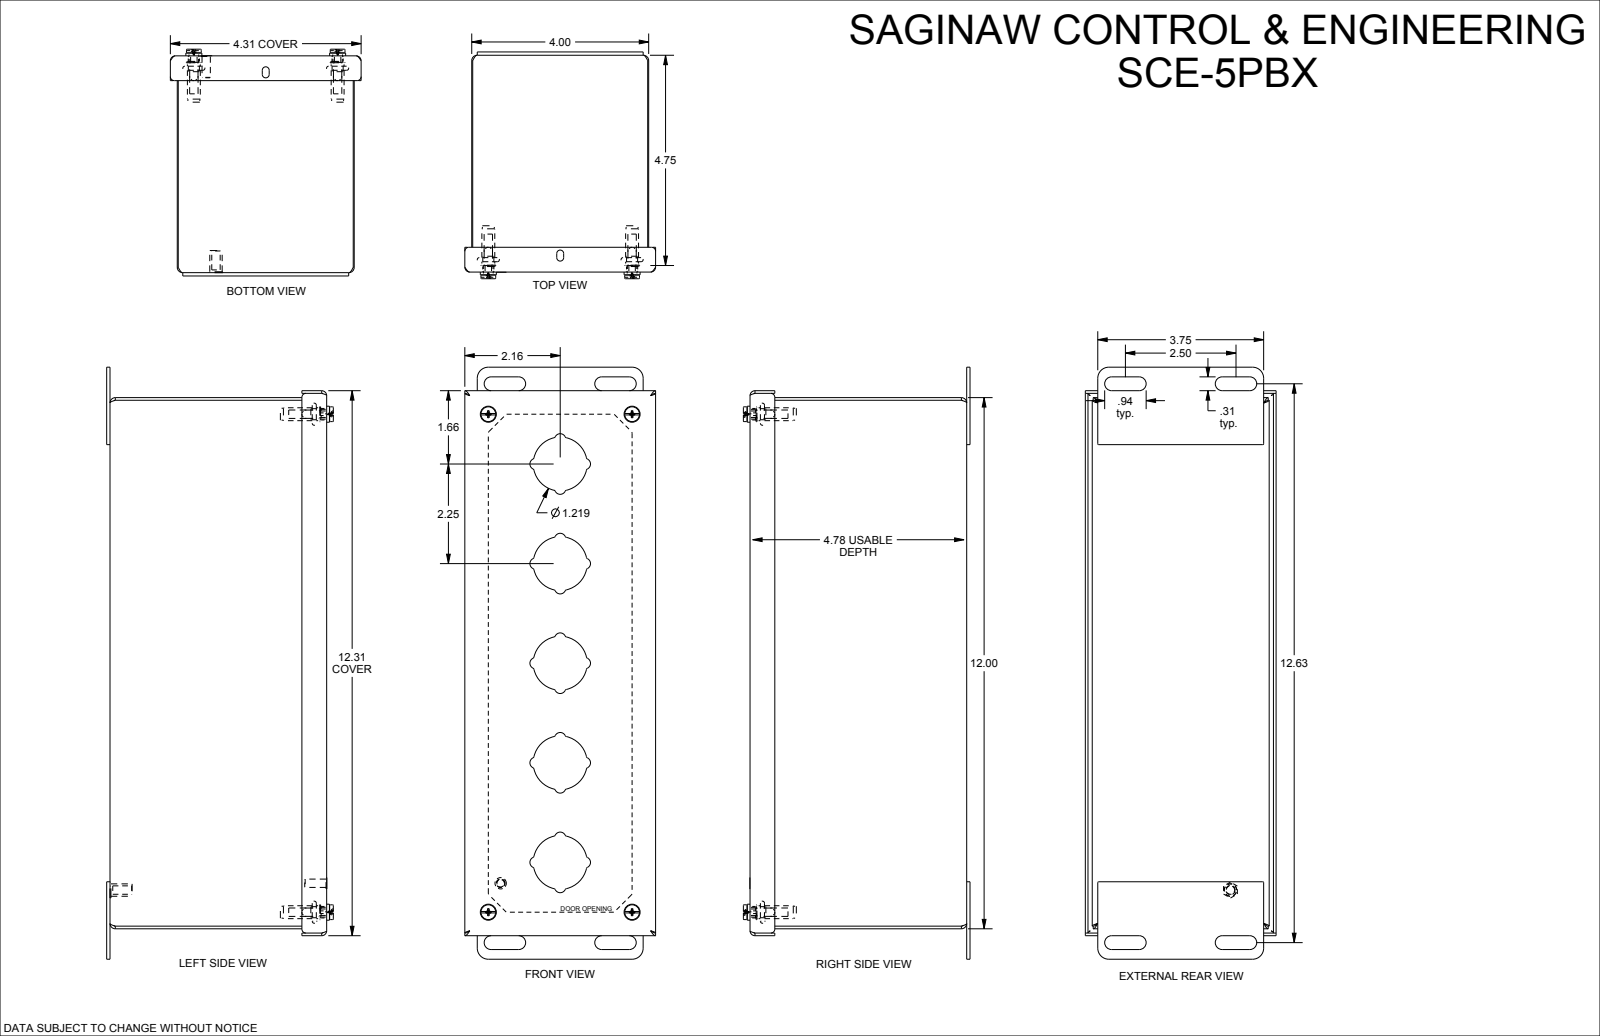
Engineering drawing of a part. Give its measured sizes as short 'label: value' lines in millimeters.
name: SCE-5PBX-RAL1018
written by: SolidWorks 2021 (AUTOMOTIVE_DESIGN)
unit: mm
bodies: 19 solids, 599 faces (209 planar, 228 cylindrical, 162 other)
size: 339.7 × 130.1 × 109.7
volume: 294 500 mm³; area: 385 900 mm²
holes: 5× ⌀4.8, 4× ⌀5.6, 4× ⌀6.4, 4× ⌀6.4, 4× ⌀8.1
bosses: 5× ⌀4.8, 4× ⌀11.1, 4× ⌀9.2, 4× ⌀8.6, 4× ⌀8.5, 4× ⌀7.4, 4× ⌀6.9, 4× ⌀6.6
rounds: 40× R1, 20× R3.2, 12× R1.5, 8× R0.4, 8× R1.6, 8× R2.9, 8× R4, 8× R6.2
face distances: 1.5, 100.1, 122.9, 101.6, 98.6, 121.4, 124.4, 303.3, 119.1, 3.8
hole spacings: 82.6, 297.4, 285.8, 82.7, 285.7, 285.8, 297.4, 71
